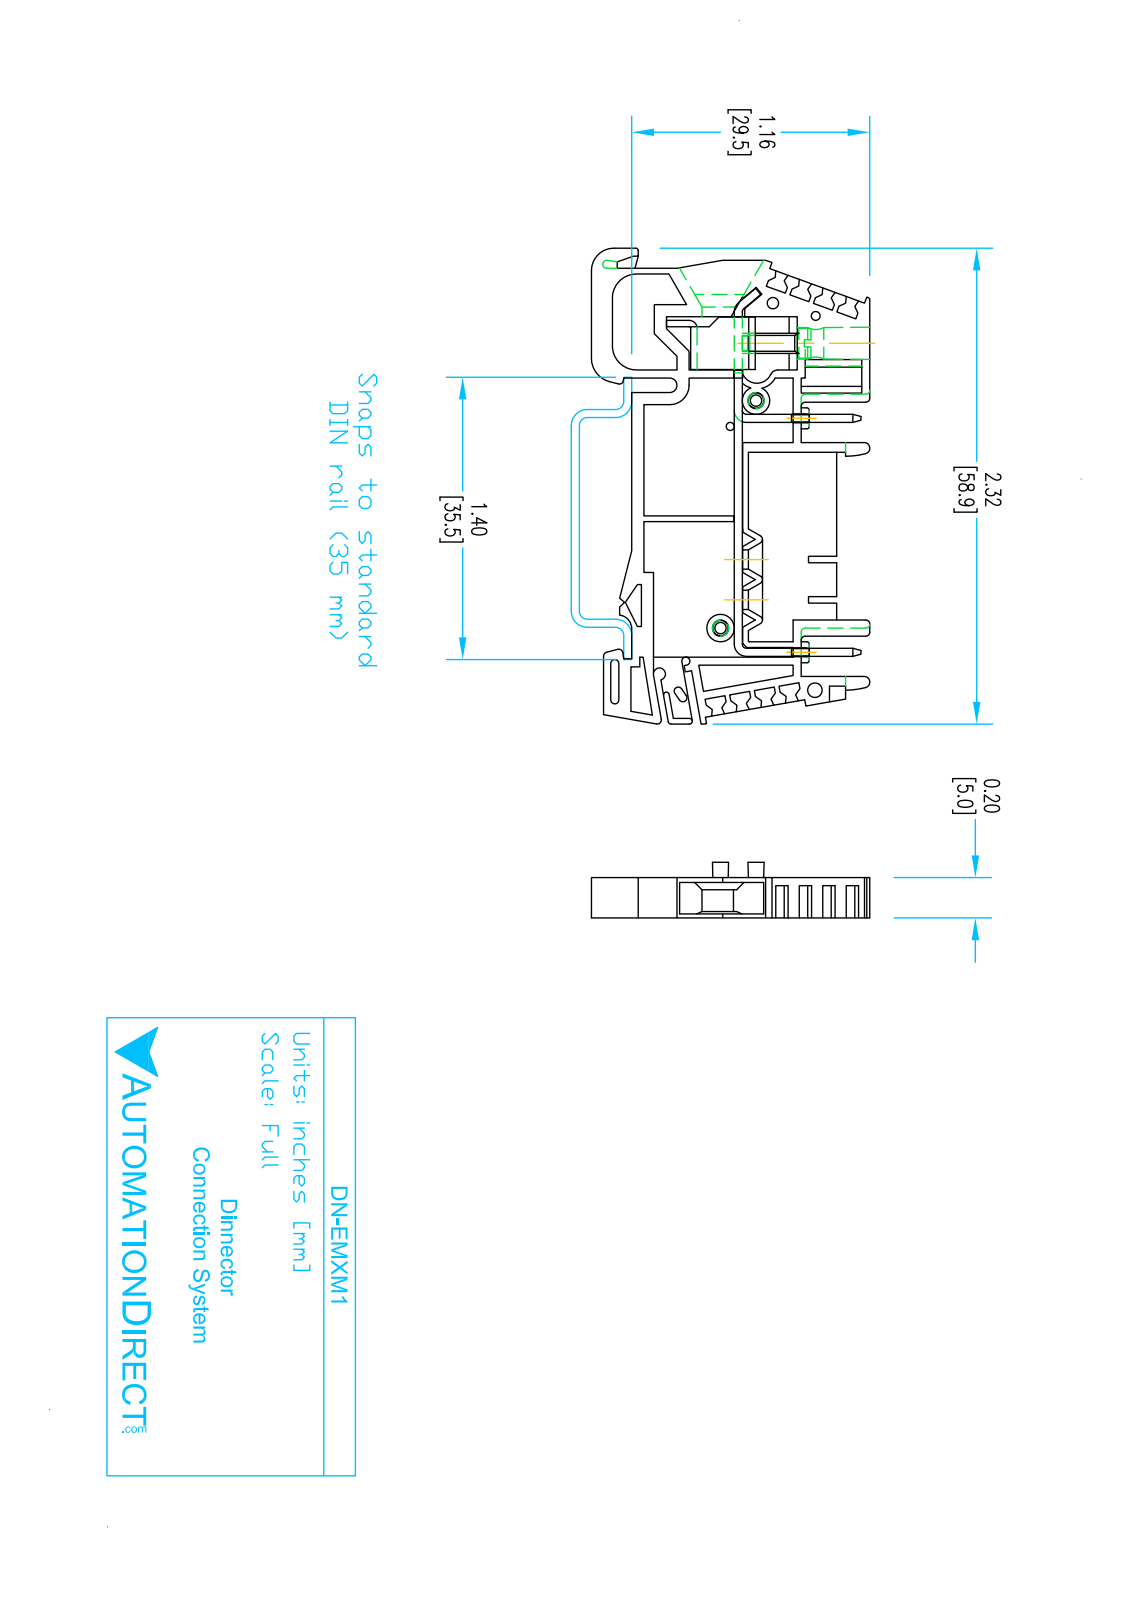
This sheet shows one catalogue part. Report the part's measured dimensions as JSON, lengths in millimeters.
{"part_name": "20450; 43560_DN-EMXM1", "step_written_by": "SolidWorks 2013 (AUTOMOTIVE_DESIGN)", "units": "millimeters", "bodies": {"solids": 1, "faces": 367, "planar": 270, "cylindrical": 76, "other": 21}, "overall_size": [59, 34.5, 6.9], "volume_mm3": 5435, "surface_area_mm2": 5595, "round_holes": [[1.1, 1], [1.4, 1], [1.8, 1], [2, 1], [4.1, 1]], "round_bosses_or_shafts": [[2.6, 2]], "partial_cylinders_radius": [[0.2, 13], [0.5, 10], [0.3, 5], [3, 5], [0.7, 2], [10, 2], [0.35, 1], [0.75, 1]], "face_to_face_distances": [5, 1, 4, 2, 3, 1.5, 2.8, 1.2, 6.2, 8.5], "hole_center_spacings": [5.54, 12.26, 12.85, 36.63, 46.4, 48.26]}
